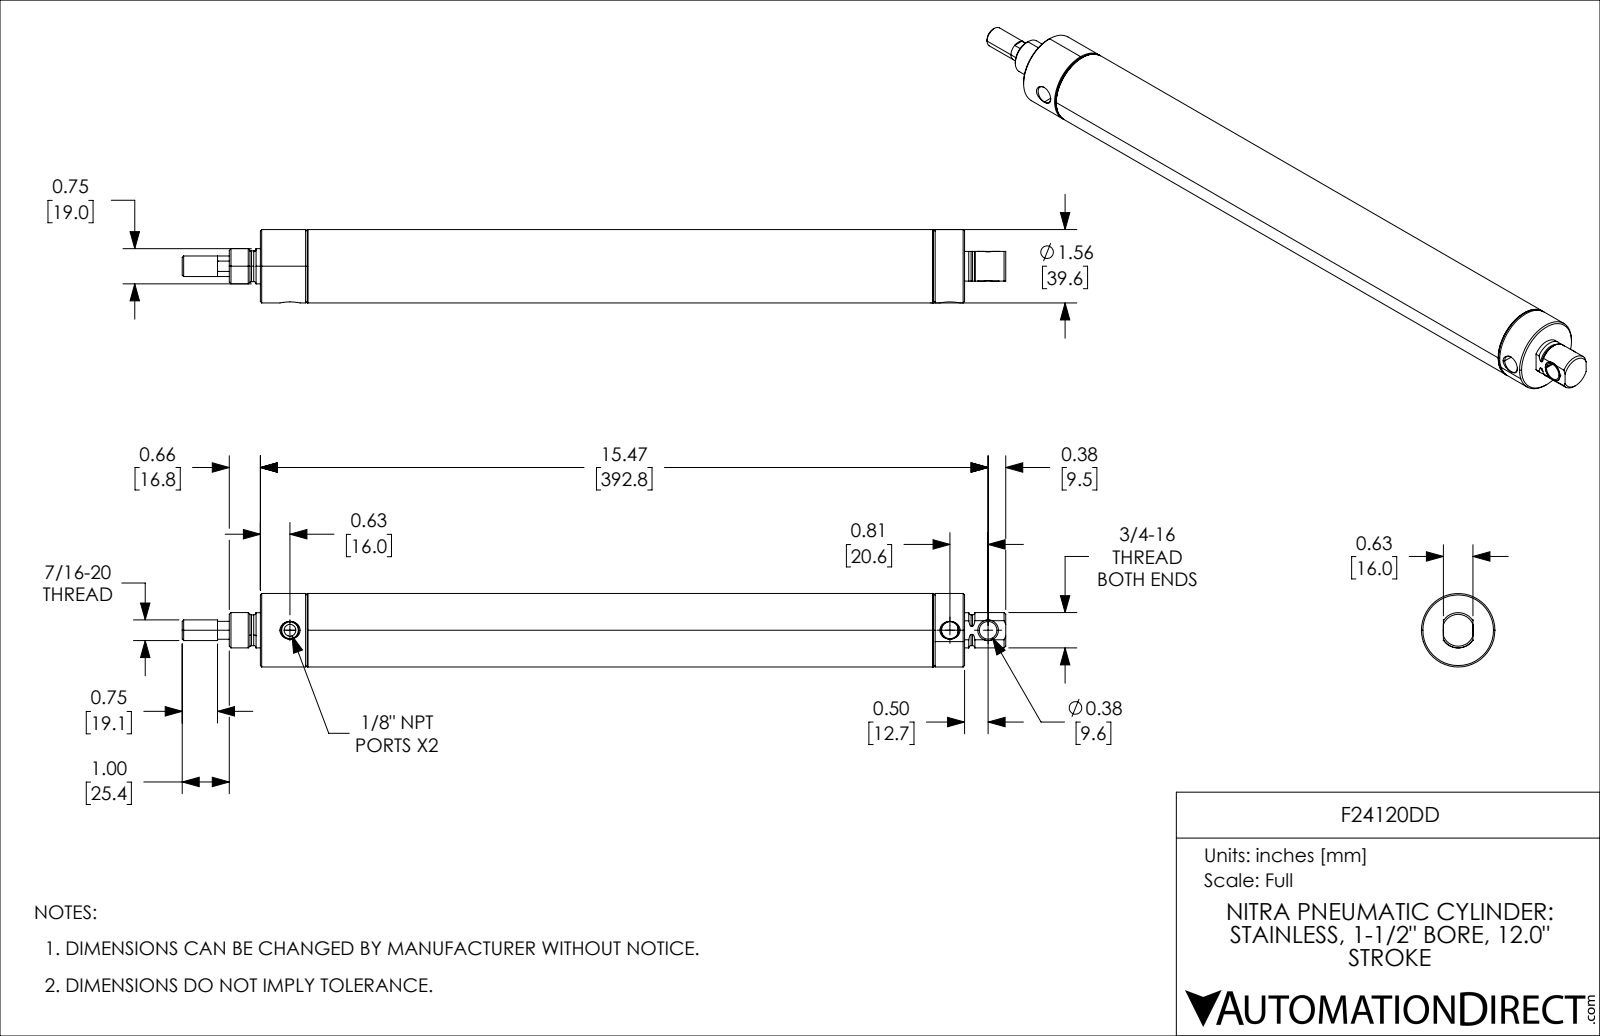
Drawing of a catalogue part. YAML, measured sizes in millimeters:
part_name: "F24120DD_9; F24120DD_3; F24120DD_7; F24120DD_5 (+2 more)"
step_written_by: "SolidWorks 2021 (CONFIG_CONTROL_DESIGN)"
units: millimeters
bodies: {solids: 5, faces: 157, planar: 35, cylindrical: 58, other: 64}
overall_size: [444.5, 39.62, 39.62]
volume: 148249
surface_area: 120970
round_holes:
  - {diameter: 6.35, count: 1}
  - {diameter: 9.14, count: 1}
  - {diameter: 9.55, count: 1}
  - {diameter: 11.15, count: 1}
  - {diameter: 11.73, count: 1}
  - {diameter: 13.51, count: 1}
  - {diameter: 26.97, count: 1}
  - {diameter: 36.36, count: 1}
round_bosses_or_shafts:
  - {diameter: 39.62, count: 1}
  - {diameter: 38.39, count: 1}
  - {diameter: 19.05, count: 1}
  - {diameter: 18.99, count: 1}
  - {diameter: 16.61, count: 1}
  - {diameter: 16.6, count: 1}
  - {diameter: 11.13, count: 1}
  - {diameter: 11.11, count: 1}
face_to_face_distances: [22.22, 44.45, 304.8, 327.02, 349.25, 22.23, 30.86, 335.66, 357.88, 380.11]
hole_center_spacings: [20.57, 356.24, 376.81]
